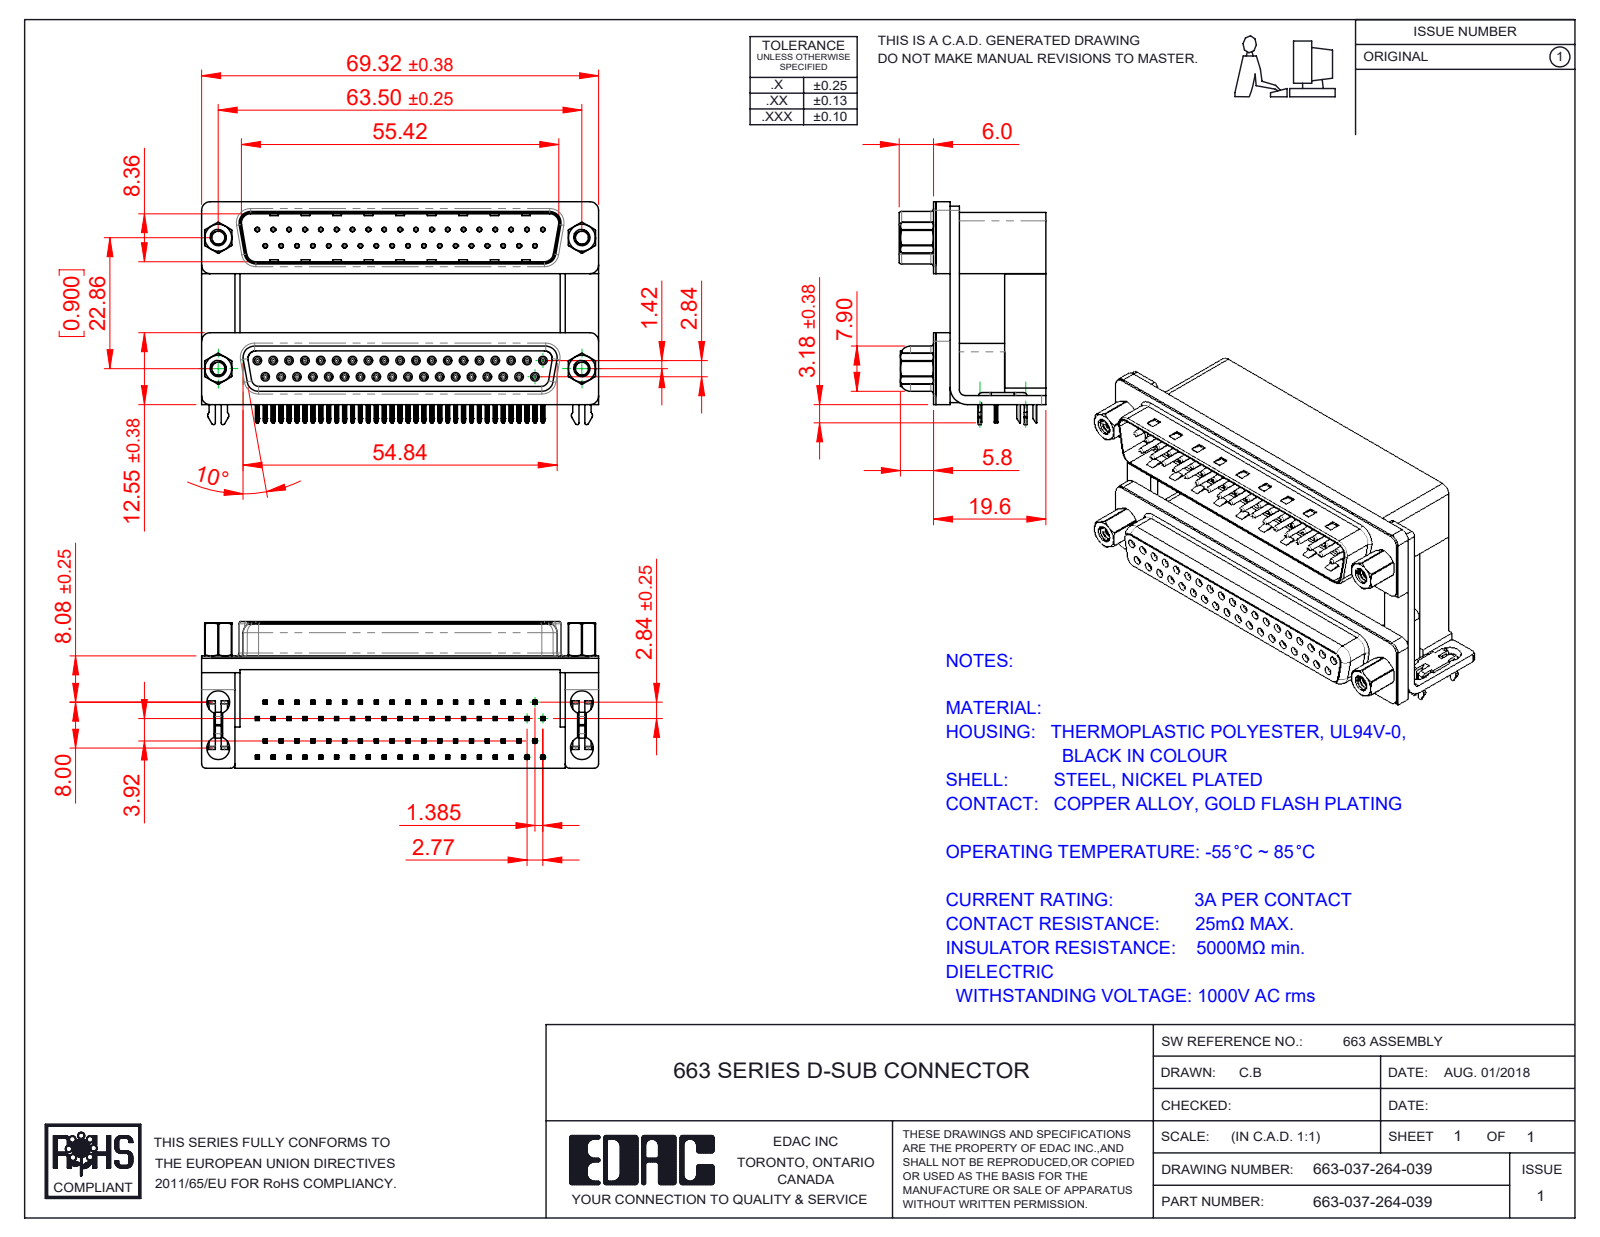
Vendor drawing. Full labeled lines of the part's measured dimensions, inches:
Part name (STEP PRODUCT): 663 Housing Spacer_37 Contacts H; 663 Shell Receptacle_37 Contacts; 663-037-264-039; 663 Threaded Rivet_4-40 (+8 more)
STEP written by: SolidWorks 2020 (CONFIG_CONTROL_DESIGN)
Units: inches
Bodies: 91 solids, 9349 faces (4887 planar, 2371 cylindrical, 2091 other)
Overall size (bounding box): 2.729 × 1.532 × 1.008
Volume: 2.028 in³ · Surface area: 54.31 in²
Round holes (diameter × count): ⌀0.031 ×74, ⌀0.014 ×37, ⌀0.035 ×37, ⌀0.157 ×8, ⌀0.089 ×4, ⌀0.09 ×4, ⌀0.138 ×4, ⌀0.189 ×4, ⌀0.197 ×4
Round bosses / shafts (diameter × count): ⌀0.047 ×37, ⌀0.03 ×37, ⌀0.193 ×4, ⌀0.187 ×4, ⌀0.154 ×4, ⌀0.11 ×4
Partial cylindrical surfaces — rounded edges, fillets, slot ends (radius × count): R0.004 ×298, R0.01 ×158, R0.006 ×148, R0.005 ×74, R0.014 ×74, R0.013 ×37, R0.011 ×18, R0.02 ×16
Main face-to-face distances: 0.756, 0.472, 0.016, 0.283, 0.112, 0.886, 0.421, 1.307, 0.421, 0.9
Hole centre spacings: 0.124, 0.109, 0.218, 0.327, 0.436, 0.545, 0.654, 0.763
